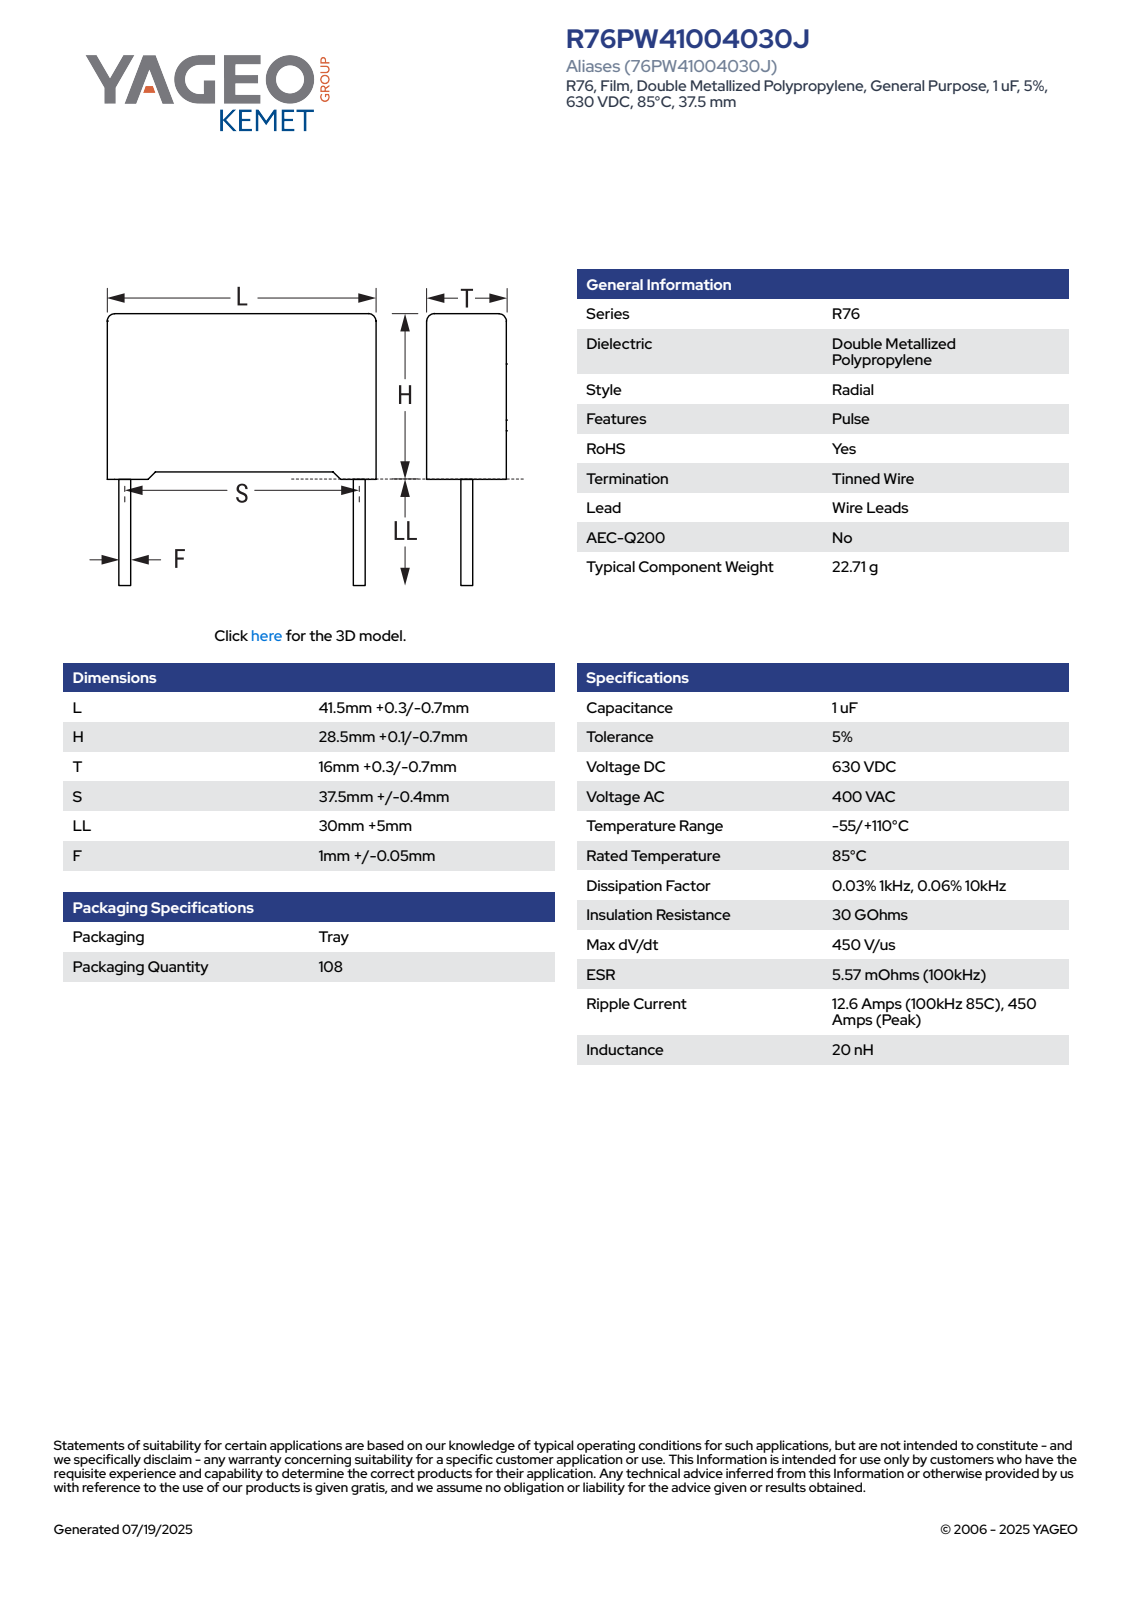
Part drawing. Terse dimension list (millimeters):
name: CFR_RB2_41.5X28.5X16_L41.8H28.6T16.3S37.5LL35F1.05
written by: SolidWorks 2021 (AUTOMOTIVE_DESIGN)
unit: mm
bodies: 4 solids, 85 faces (77 planar, 8 cylindrical, 0 other)
size: 63.6 × 41.8 × 16.3
volume: 18 952 mm³; area: 4 994 mm²
bosses: 2× ⌀1.05
rounds: 4× R0.5
face distances: 16.3, 27.61, 41.8, 27.85, 0.75, 0.99, 28.6, 16.31, 1.39, 40.41
